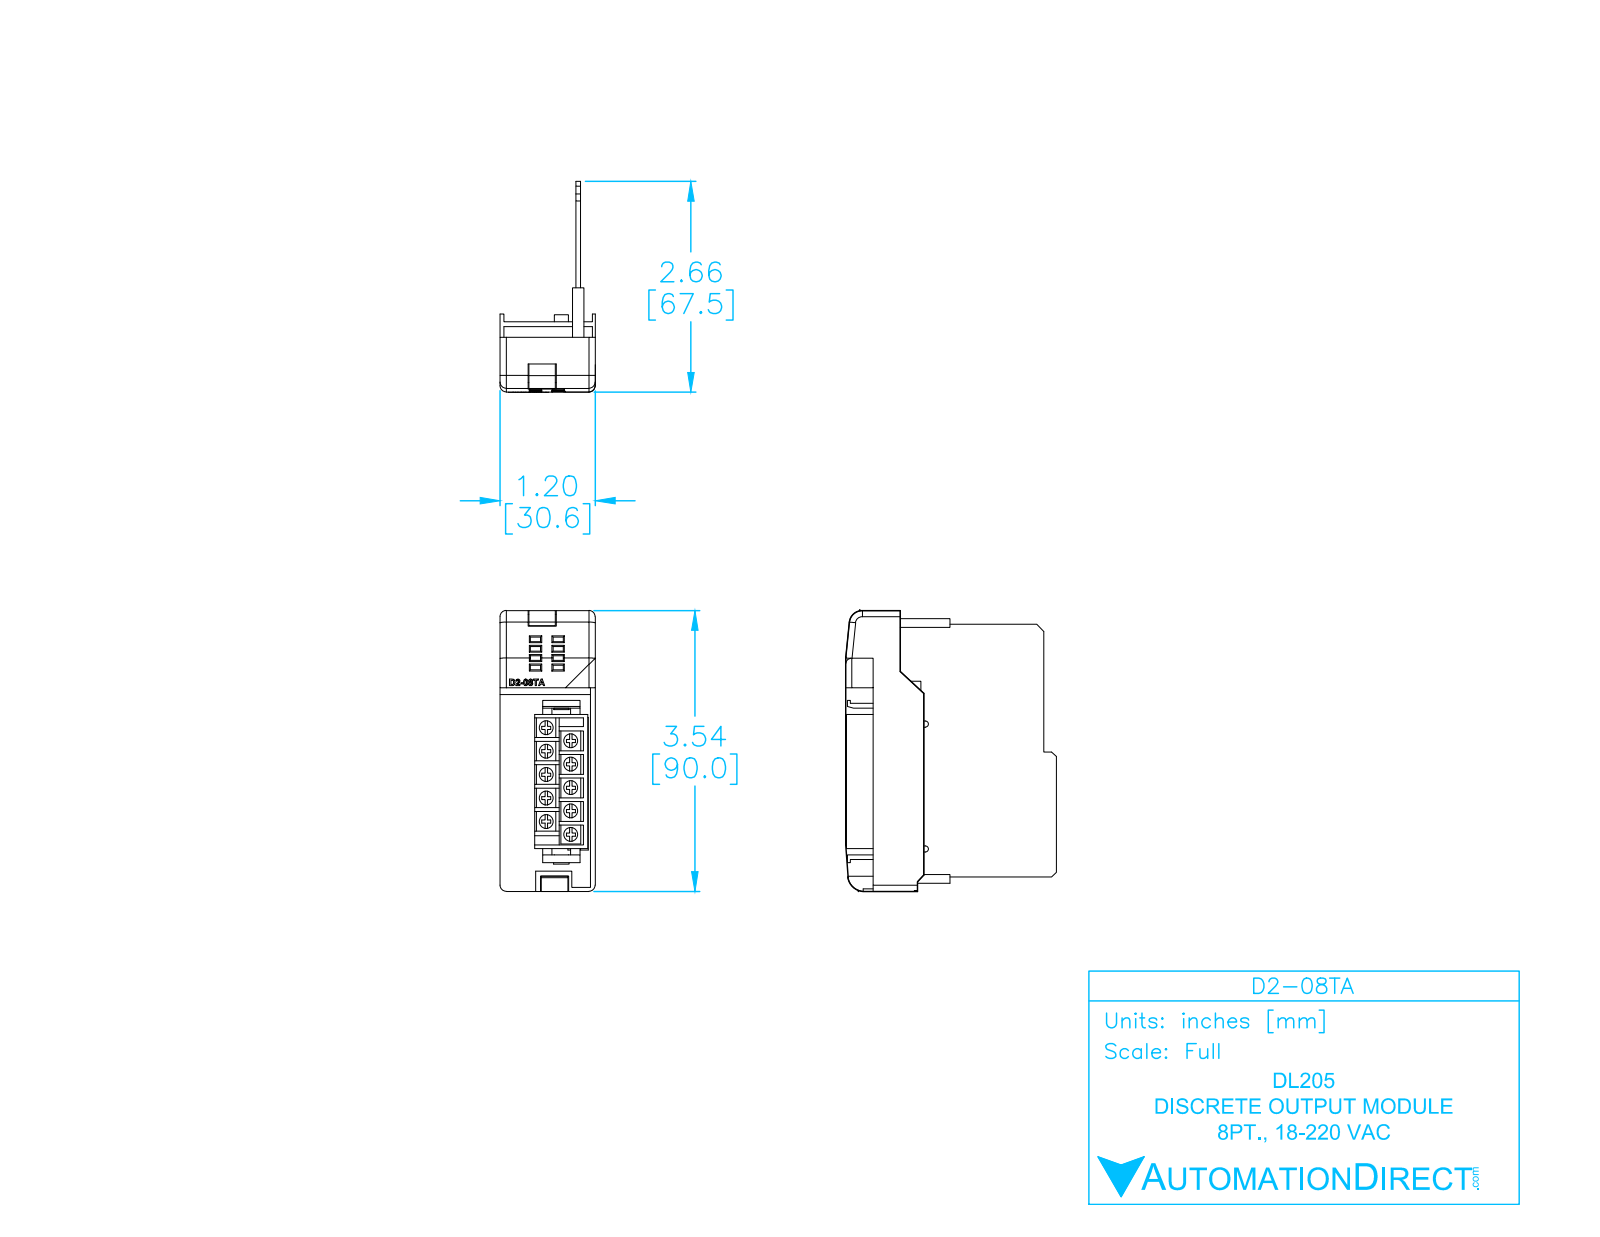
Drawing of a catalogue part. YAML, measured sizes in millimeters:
part_name: "D2-08TA_ModuleCase_light_NEW"
step_written_by: "SolidWorks 2009 (AUTOMOTIVE_DESIGN)"
units: millimeters
bodies: {solids: 6, faces: 565, planar: 399, cylindrical: 75, other: 91}
overall_size: [90, 67.56, 30.55]
volume: 25372
surface_area: 28529
round_bosses_or_shafts:
  - {diameter: 4.5, count: 10}
partial_cylinders:
  - {radius: 0.35, count: 16}
  - {radius: 2, count: 9}
  - {radius: 0.25, count: 2}
  - {radius: 1, count: 2}
  - {radius: 1.25, count: 2}
  - {radius: 4.12, count: 1}
  - {radius: 5.39, count: 1}
face_to_face_distances: [1.5, 4.72, 6.22, 2.37, 3.87, 2.35, 3.22, 0.85, 8.14, 24.28]
